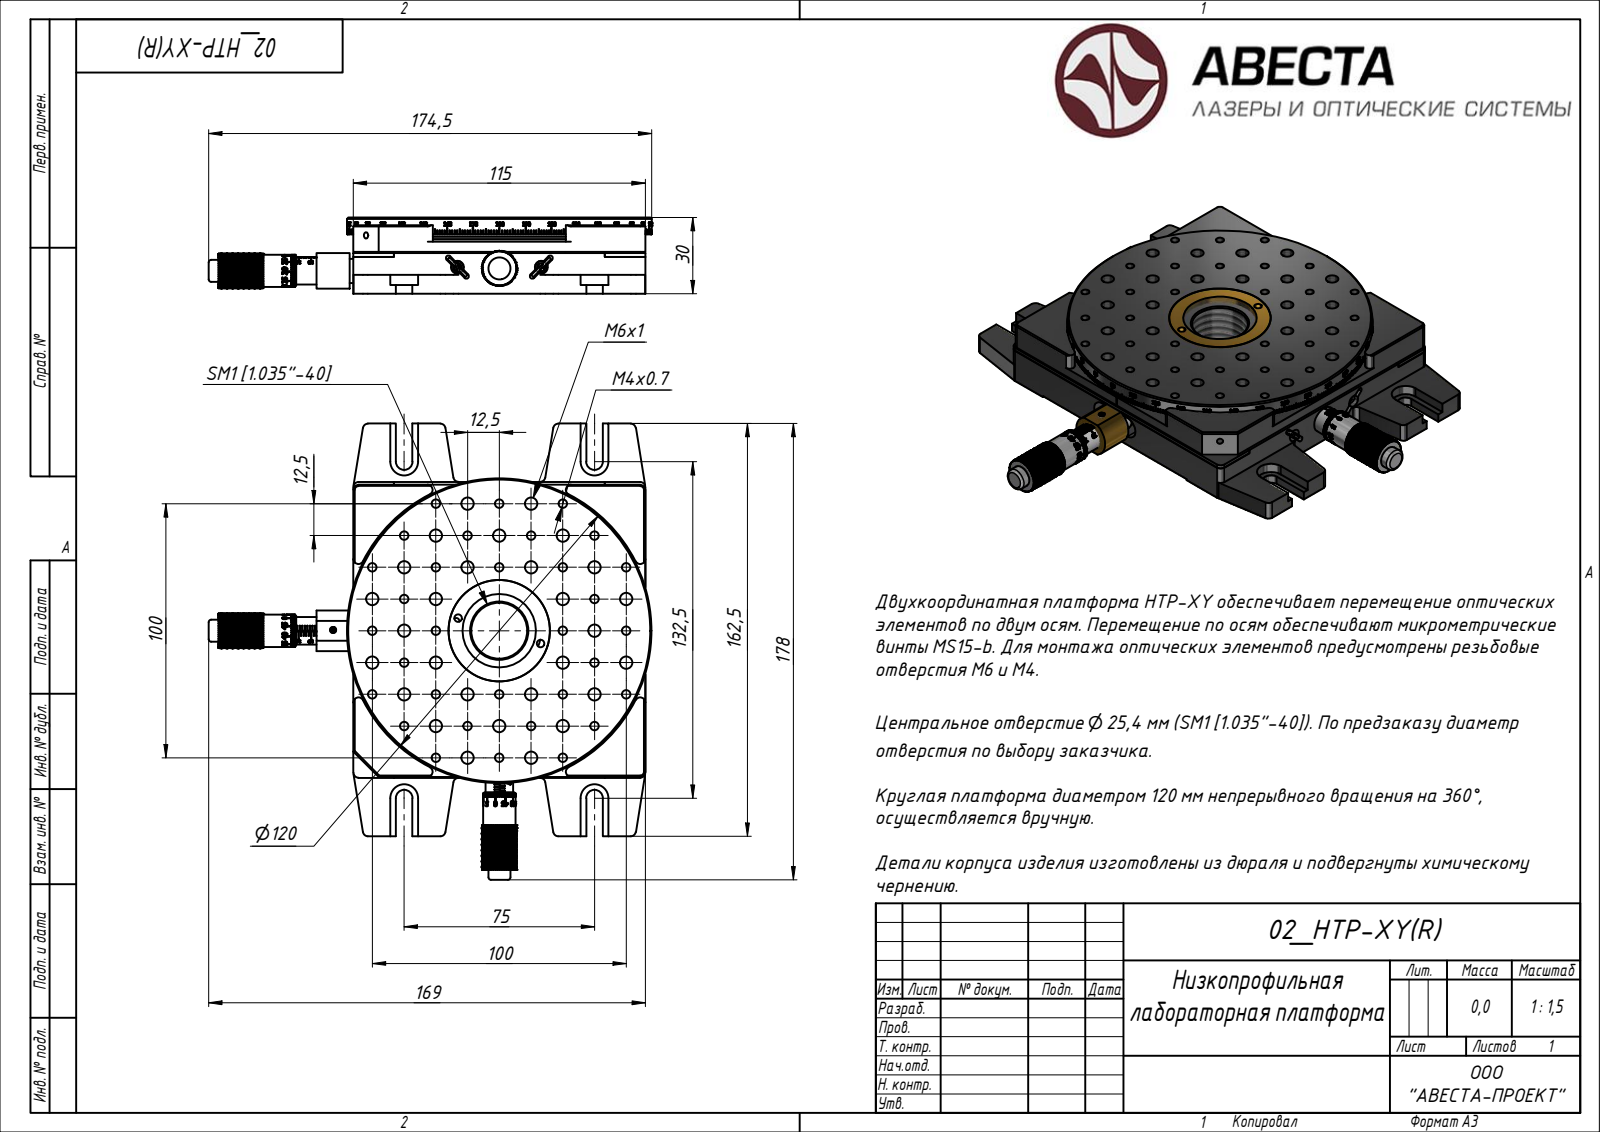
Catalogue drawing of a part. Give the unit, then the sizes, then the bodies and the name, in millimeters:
Units: millimetres
Overall size (bounding box): 179.58 × 174.5 × 30
Round holes (diameter × count): ⌀3.24 ×32, ⌀4.92 ×21, ⌀2.46 ×18, ⌀3.5 ×10, ⌀1.57 ×6, ⌀2.3 ×6, ⌀5 ×6, ⌀4 ×4, ⌀3 ×2, ⌀3.1 ×2, ⌀5.5 ×2, ⌀8 ×2
Round bosses / shafts (diameter × count): ⌀0.7 ×6, ⌀3 ×4, ⌀13.5 ×2, ⌀12.7 ×2, ⌀10.8 ×2, ⌀8.66 ×2, ⌀3.2 ×2, ⌀2 ×2
Partial cylindrical surfaces — rounded edges, fillets, slot ends (radius × count): R2 ×63, R0.19 ×10, R0.29 ×10, R1.23 ×10, R1.23 ×10, R1 ×8, R2.46 ×7, R2.46 ×7
Main face-to-face distances: 3, 4, 0.5, 3.5, 16, 7, 20, 12.5, 16.5, 13.5
Hole centre spacings: 19.56, 39, 0.5, 99, 17.25, 24.25, 32.6, 36.25
Volume: 314 546 mm³ · Surface area: 132 569 mm²
Bodies: 11 solids, 10319 faces (7239 planar, 1341 cylindrical, 1739 other)
STEP written by: Rhino 7.34 (AUTOMOTIVE_DESIGN)
